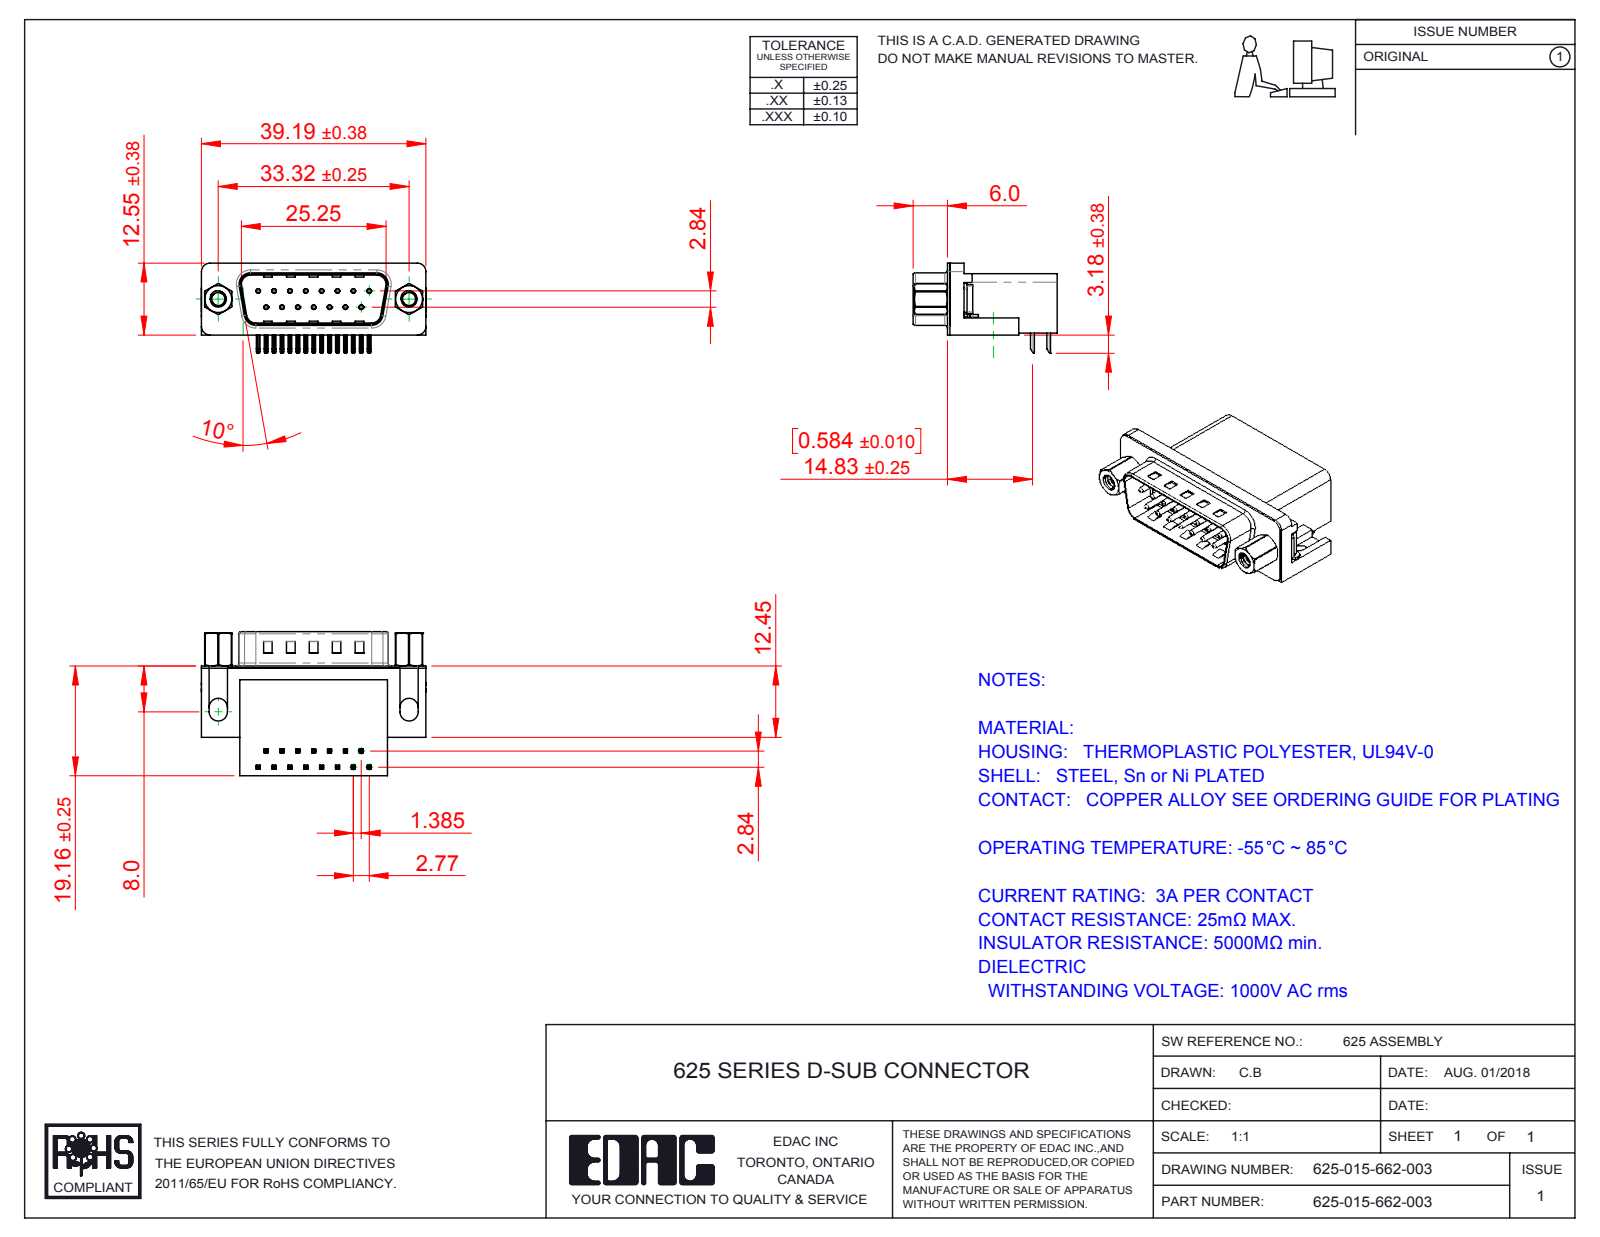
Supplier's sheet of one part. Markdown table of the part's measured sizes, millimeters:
| quantity | value |
| --- | --- |
| part name | 625 Housing_15 Socket; 625 4-40 Hex Standoff 5; 625 Shell_15 Socket; 625 4-40 Threaded Rivet (+4 more) |
| STEP written by | SolidWorks 2016 (CONFIG_CONTROL_DESIGN) |
| units | millimeters |
| bodies | 23 solids, 1603 faces (917 planar, 515 cylindrical, 171 other) |
| overall size | 39.22 × 25.16 × 15.73 |
| volume | 6 429 mm³ |
| surface area | 6 773 mm² |
| round holes (diameter × count) | 0.35 × 15, 0.8 × 15, 2.26 × 2, 2.29 × 2, 4 × 2, 4.8 × 2, 5 × 2 |
| round bosses / shafts (diameter × count) | 0.75 × 15, 4.9 × 2, 4.75 × 2, 3.9 × 2, 2.79 × 2 |
| partial cylindrical surfaces (radius × count) | 0.25 × 68, 0.12 × 30, 1 × 16, 0.5 × 9, 1.6 × 8, 1.5 × 6, 0.9 × 4, 2 × 4 |
| main face-to-face distances | 0.4, 10.35, 18.76, 2.1, 19.16, 10.46, 1.7, 10.86, 8.76, 16.26 |
| hole center spacings | 3.16, 2.77, 5.54, 8.31, 11.08, 5.03, 5.04, 7.48 |
